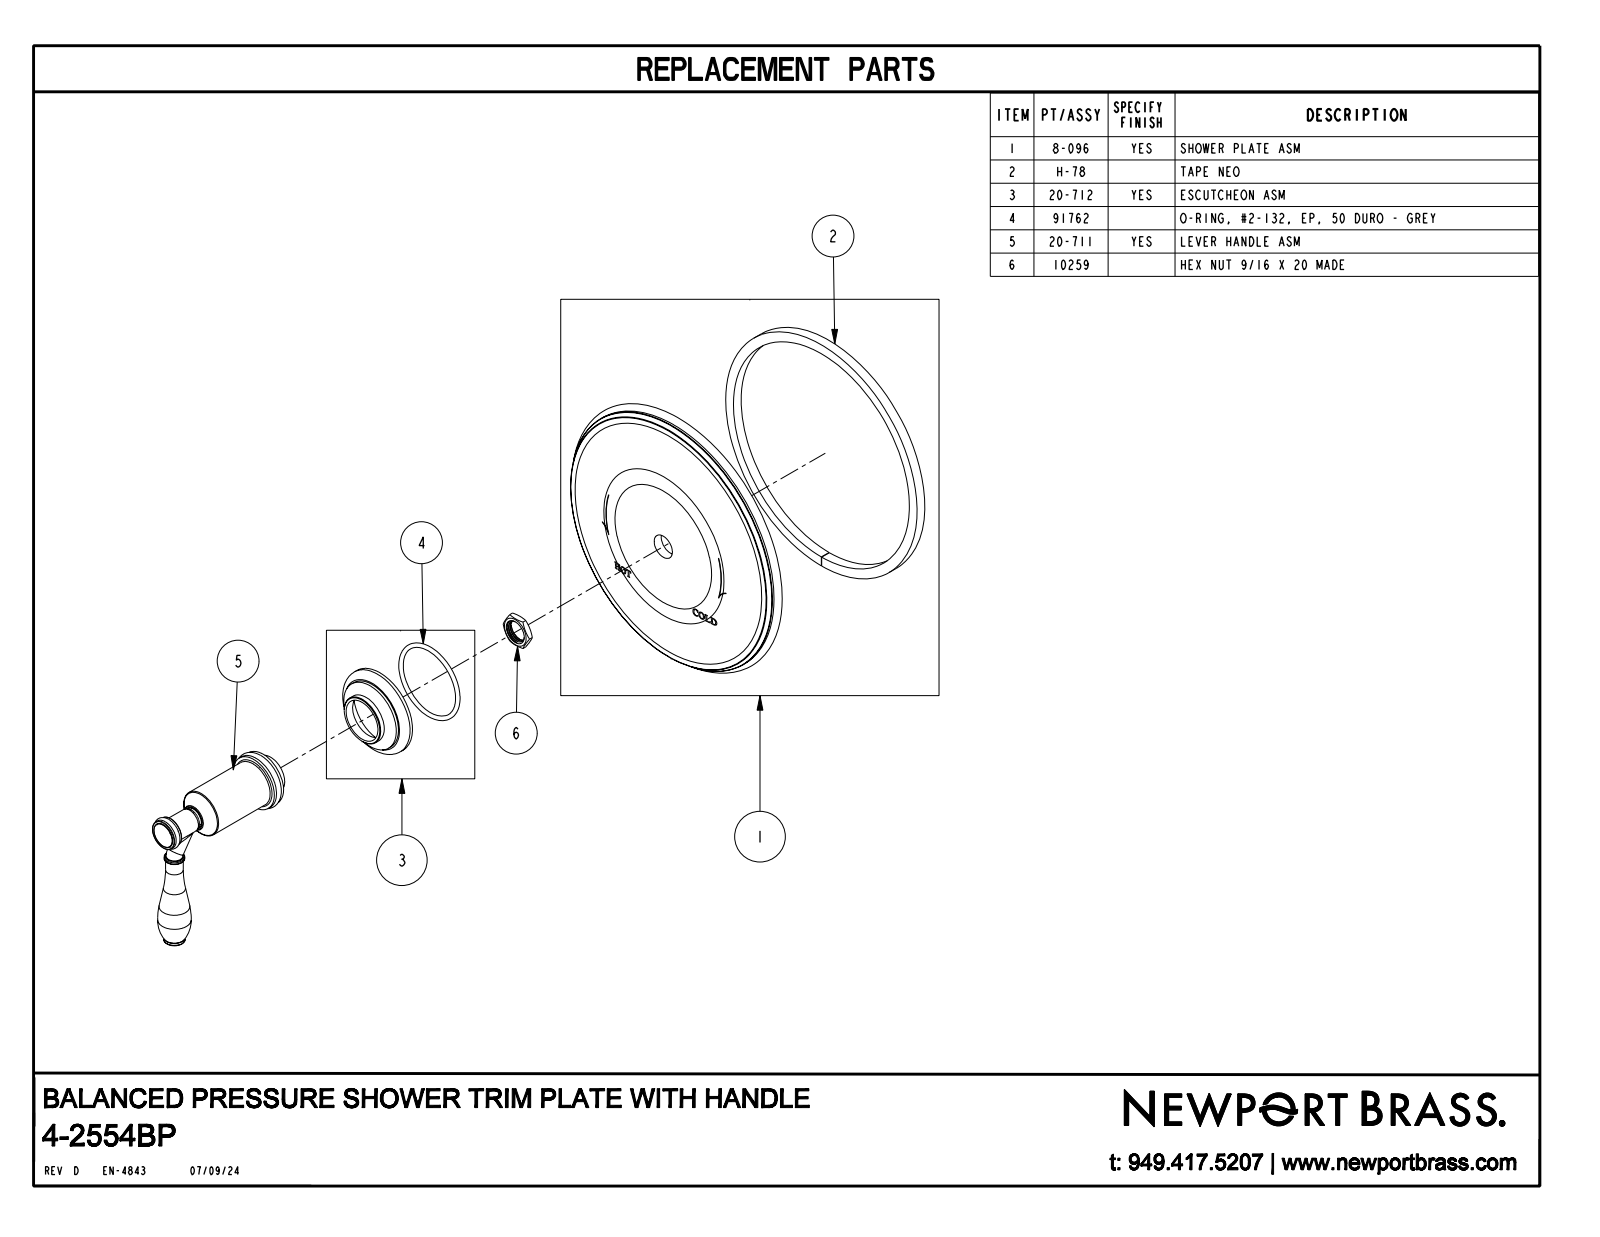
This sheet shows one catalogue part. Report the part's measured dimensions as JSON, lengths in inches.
{"part_name": "4-2554BP", "step_written_by": "CREO PARAMETRIC BY PTC INC, 2018400 (CONFIG_CONTROL_DESIGN)", "units": "inches", "bodies": {"solids": 1, "faces": 105, "planar": 12, "cylindrical": 30, "other": 63}, "overall_size": [6.75, 6.75, 4.241], "volume_in3": 18.19, "surface_area_in2": 93.18, "round_bosses_or_shafts": [[6.51, 1], [2.11, 1], [1.7, 1], [1.33, 1], [1.12, 1], [0.714, 1], [0.6, 1], [0.57, 1]], "face_to_face_distances": [0.48, 0.313, 0.167, 0.93, 0.617, 0.45, 1.23, 0.917, 0.75, 0.3]}
